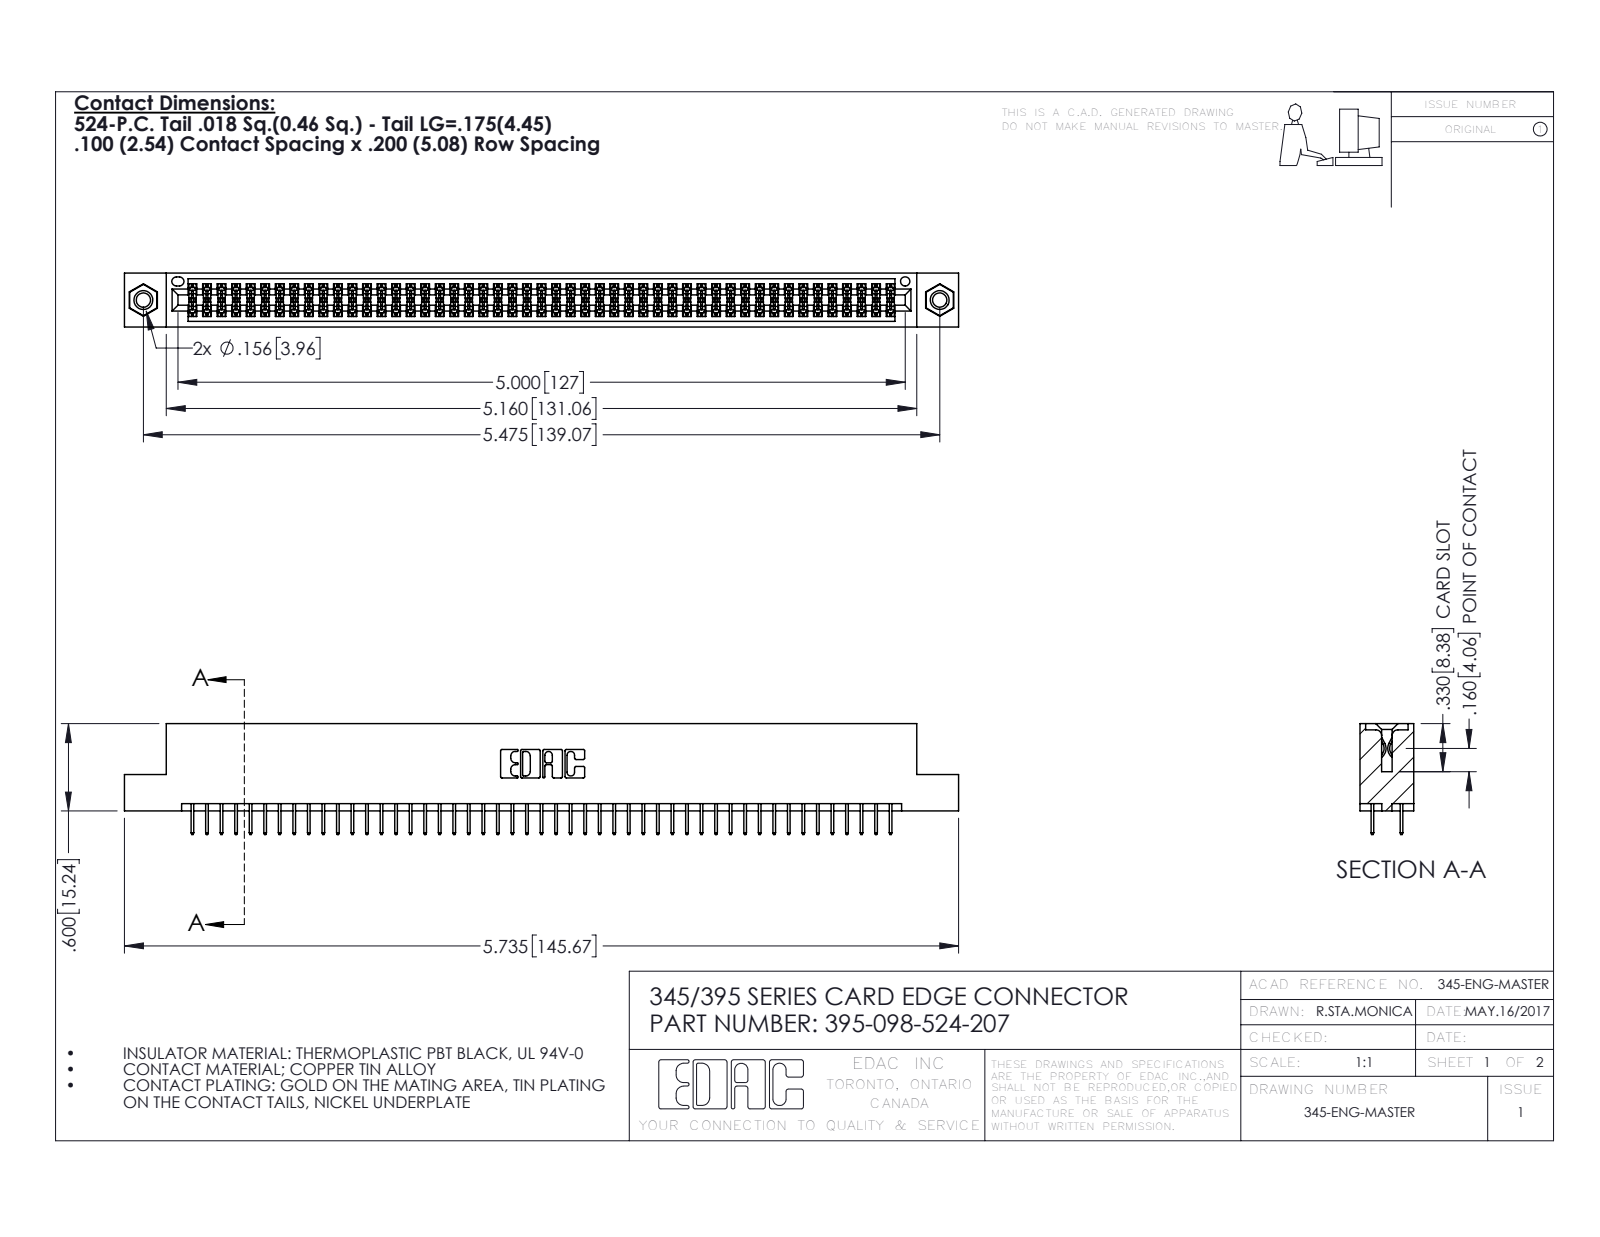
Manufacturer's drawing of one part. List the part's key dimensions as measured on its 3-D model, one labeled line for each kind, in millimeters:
Part name (STEP PRODUCT): 395-098-524-207; 345-250-001_345-250-005-103; 345-292-001_345-293-124; 345 Part_Flush Mounting Lugs - 0.156 Dia-TI
STEP written by: SolidWorks 2016 (CONFIG_CONTROL_DESIGN)
Units: millimetres
Bodies: 101 solids, 5478 faces (3934 planar, 1528 cylindrical, 16 other)
Overall size (bounding box): 145.7 × 19.4 × 9.4
Volume: 14 100 mm³ · Surface area: 20 550 mm²
Round holes (diameter × count): ⌀2.5 ×2, ⌀3.2 ×2, ⌀4 ×2, ⌀1.6 ×1
Round bosses / shafts (diameter × count): ⌀3.9 ×2
Partial cylindrical surfaces — rounded edges, fillets, slot ends (radius × count): R0.2 ×147, R0.3 ×22, R0.2 ×6, R0.8 ×6, R0.7 ×3, R0.4 ×2, R0.5 ×2, R0.6 ×2
Main face-to-face distances: 1.8, 7.6, 5.1, 9.4, 2.5, 6.9, 0.6, 5.7, 1.8, 4.4
Hole centre spacings: 6.9, 133.1, 139.1
